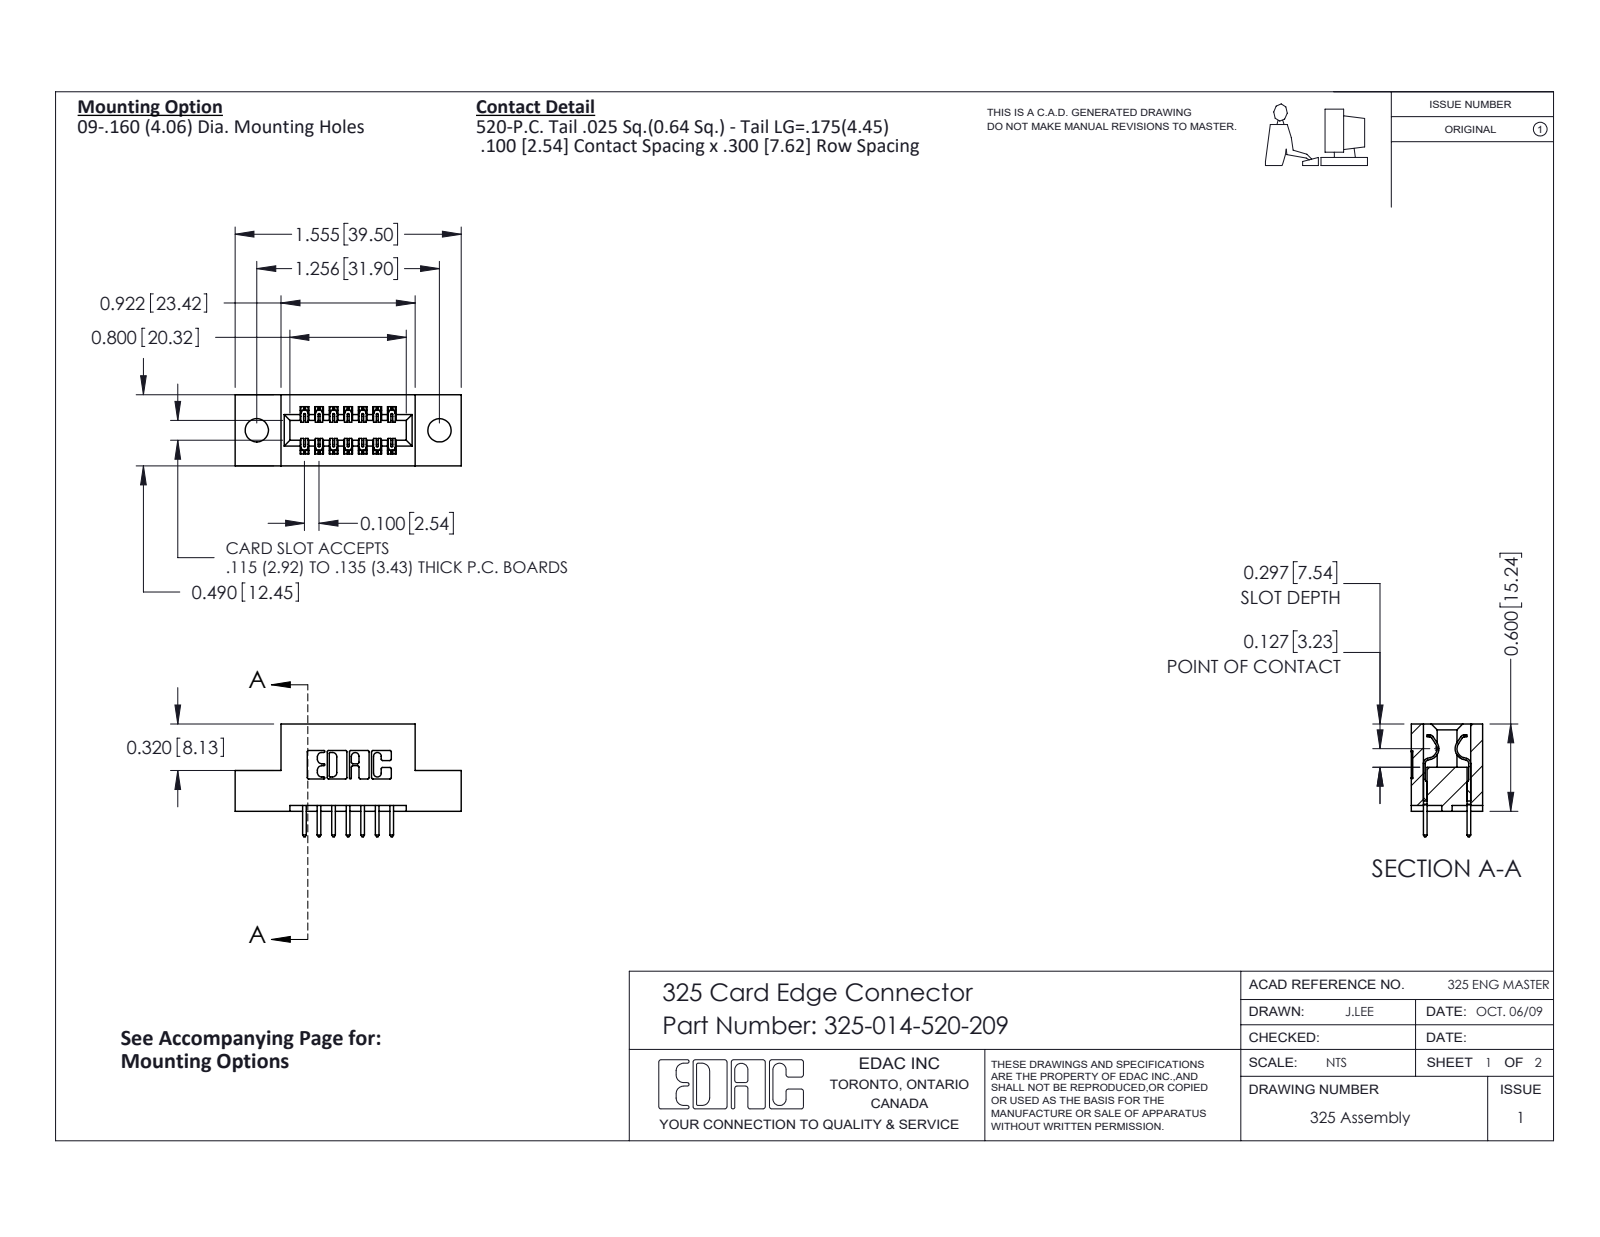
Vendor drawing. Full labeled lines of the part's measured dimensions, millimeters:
Part name (STEP PRODUCT): 325 Part_.160 TH; 325-014-520-209; 325-292-001_325-293-120
STEP written by: SolidWorks 2016 (CONFIG_CONTROL_DESIGN)
Units: millimetres
Bodies: 15 solids, 842 faces (574 planar, 268 cylindrical, 0 other)
Overall size (bounding box): 39.5 × 19.7 × 12.4
Volume: 4 560 mm³ · Surface area: 4 572 mm²
Round holes (diameter × count): ⌀4.1 ×2
Partial cylindrical surfaces — rounded edges, fillets, slot ends (radius × count): R0.3 ×22, R0.2 ×21, R0.3 ×14, R0.2 ×6, R0.8 ×6, R0.7 ×3, R0.4 ×2, R0.6 ×2
Main face-to-face distances: 7.6, 2.5, 2.1, 10.3, 1, 5.1, 12.4, 1.5, 4.1, 10.2
Hole centre spacings: 31.9
